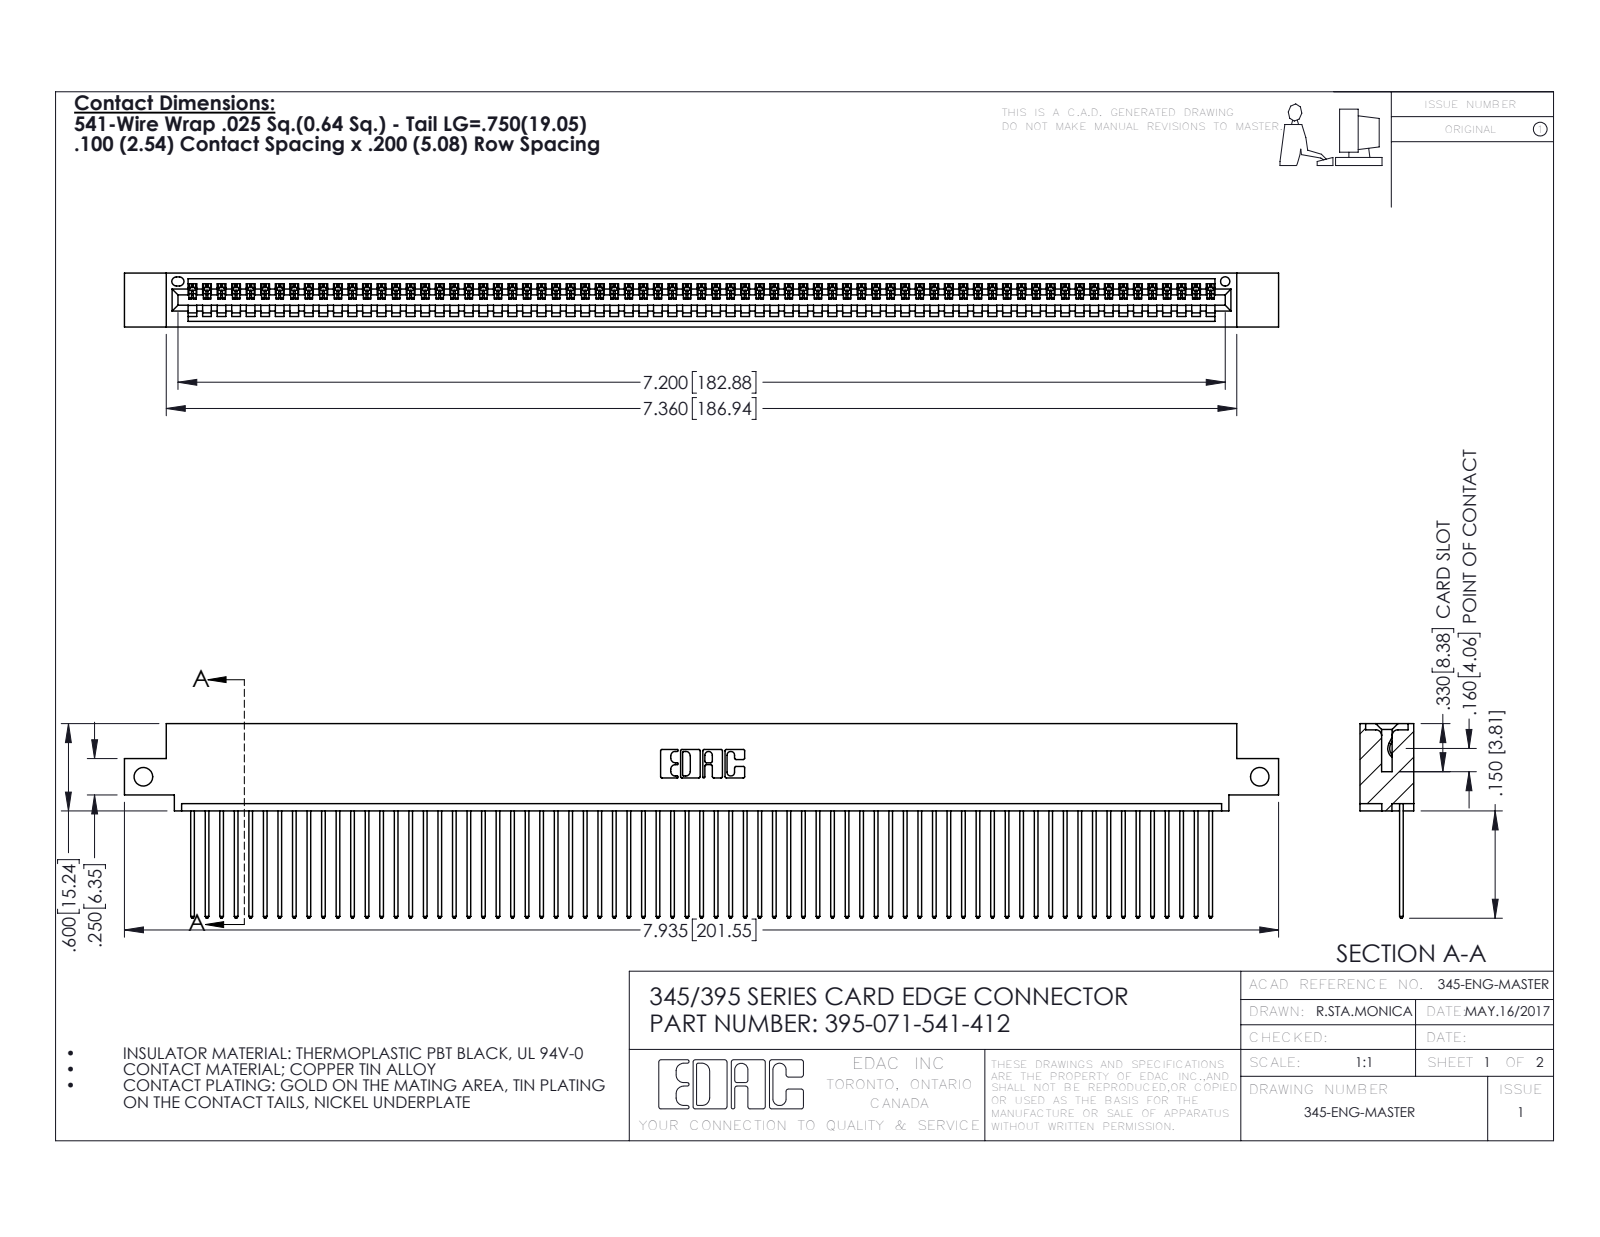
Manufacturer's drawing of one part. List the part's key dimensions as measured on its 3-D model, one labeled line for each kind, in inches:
Part name (STEP PRODUCT): 345-292-001_345-293-141; 395-071-541-412; 345 Part_0.110 Offset - Side Mount
STEP written by: SolidWorks 2016 (CONFIG_CONTROL_DESIGN)
Units: inches
Bodies: 72 solids, 4248 faces (2924 planar, 1324 cylindrical, 0 other)
Overall size (bounding box): 7.935 × 1.337 × 0.37
Volume: 1.187 in³ · Surface area: 42.73 in²
Round holes (diameter × count): ⌀0.128 ×2, ⌀0.064 ×1
Partial cylindrical surfaces — rounded edges, fillets, slot ends (radius × count): R0.006 ×142, R0.01 ×142, R0.01 ×22, R0.007 ×6, R0.031 ×6, R0.026 ×3, R0.031 ×2, R0.04 ×2
Main face-to-face distances: 0.072, 0.298, 0.098, 0.272, 0.025, 0.37, 0.2, 0.225, 0.149, 0.072
Hole centre spacings: 7.675
